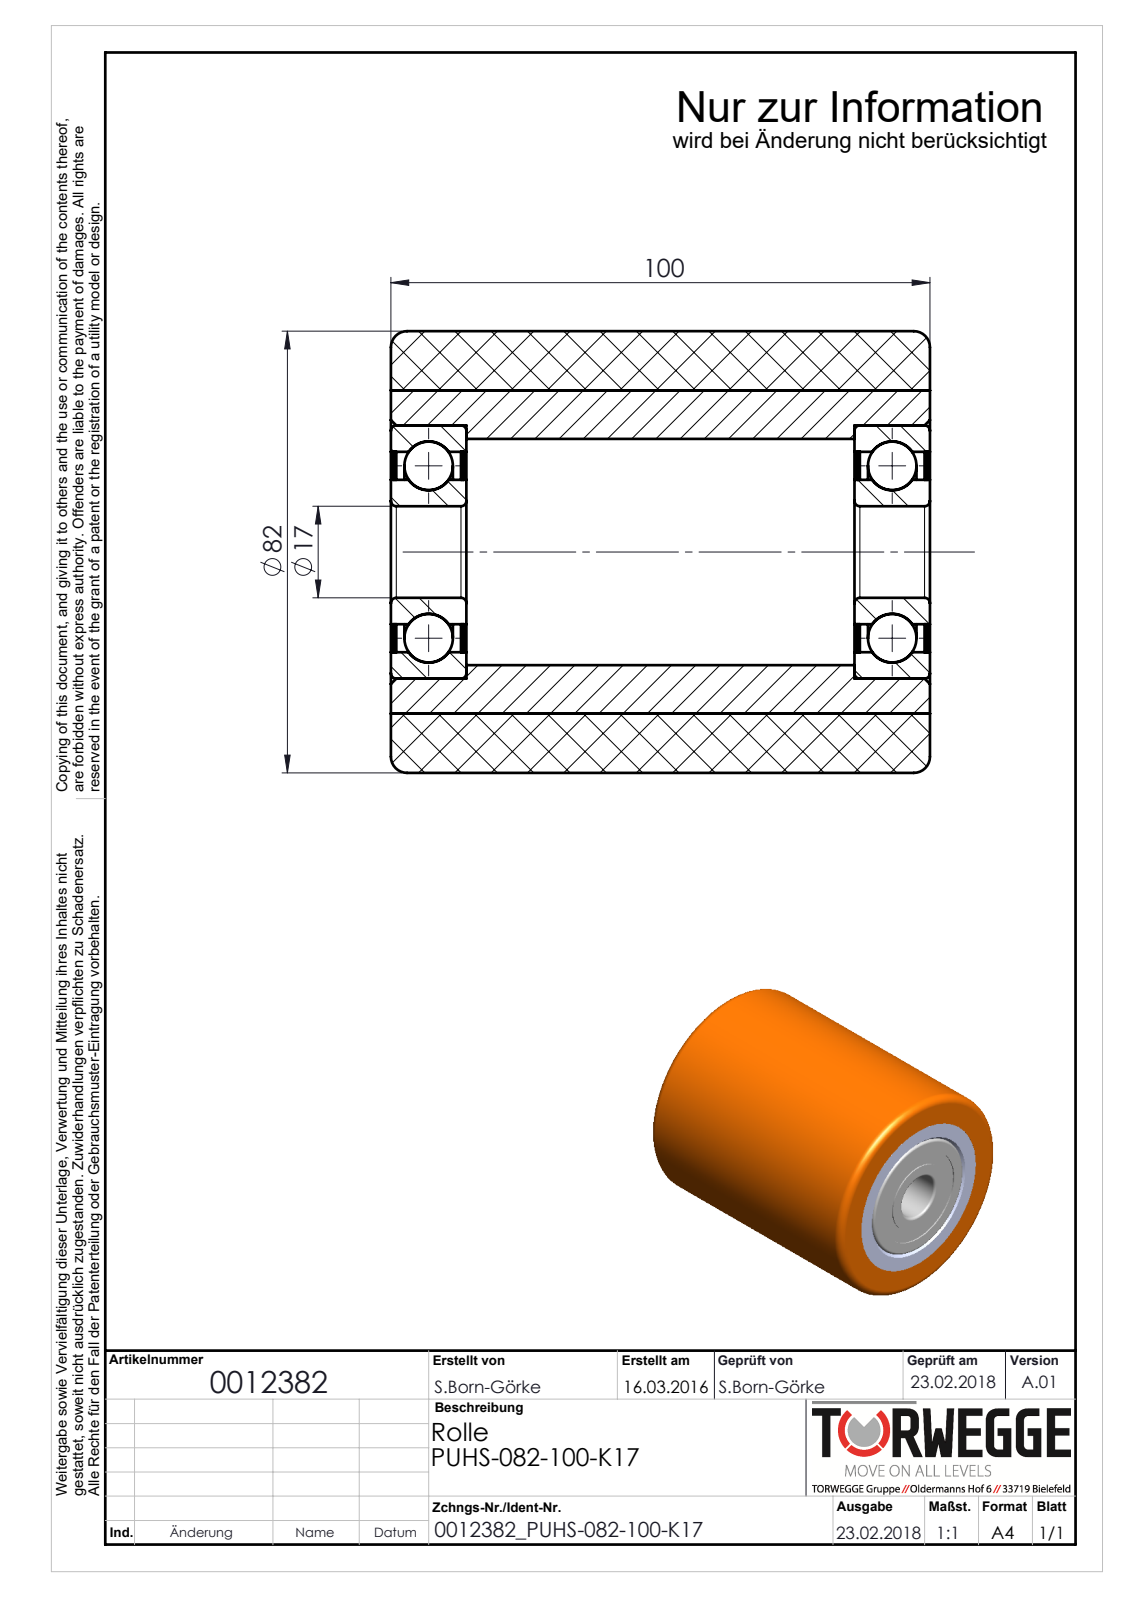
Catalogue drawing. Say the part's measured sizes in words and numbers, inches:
The part is named "0012382_PUHS-082-100-K17". Its 3-D file was written by "SolidWorks 2016 (AUTOMOTIVE_DESIGN)". It is 12 solids with 118 faces: 22 planar, 52 cylindrical and 44 other. Overall it measures 3.937 by 3.228 by 3.228 inches. Its volume is 25.36 cubic inches and its surface area 170 square inches. Round holes: 1 of diameter 0.669, 1 of diameter 1.055, 1 of diameter 1.465, 1 of diameter 1.654, 1 of diameter 1.85, 1 of diameter 2.362. Round bosses or shafts: 1 of diameter 3.228. The main face-to-face distances are 3.386, 0.02, 3.937, 0.512, 0.551, 0.039, 0.531, 3.406, 0.492, 3.366.
